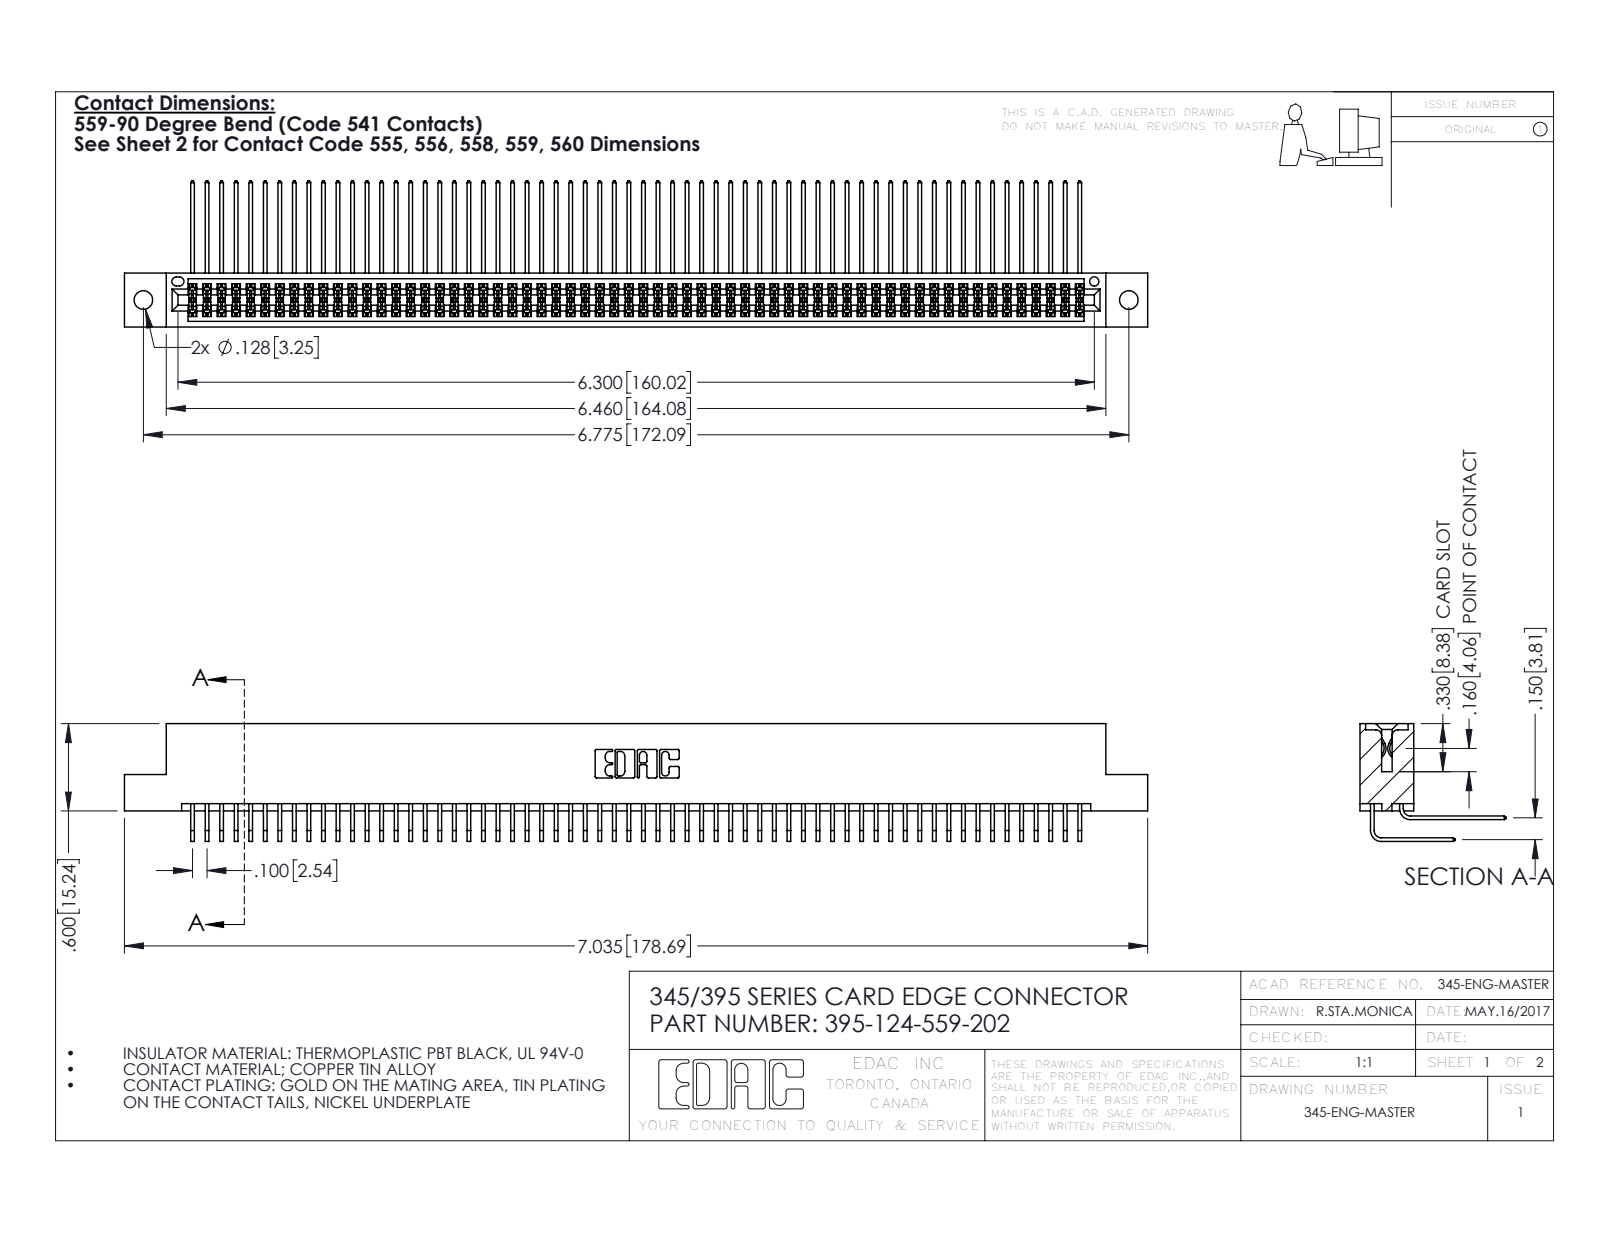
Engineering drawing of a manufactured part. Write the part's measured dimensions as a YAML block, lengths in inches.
part_name: "395-124-559-202; 345 Part_Flush Mounting Lugs - 0.128 Dia; 345-292-001_558 559 Tail - 1; 345-292-001_559 Tail - 2"
step_written_by: "SolidWorks 2016 (CONFIG_CONTROL_DESIGN)"
units: inches
bodies: {solids: 125, faces: 6574, planar: 4420, cylindrical: 2154, other: 0}
overall_size: [7.035, 1.005, 0.809]
volume: 1.112
surface_area: 47.14
round_holes:
  - {diameter: 0.128, count: 2}
  - {diameter: 0.064, count: 1}
partial_cylinders:
  - {radius: 0.006, count: 187}
  - {radius: 0.01, count: 22}
  - {radius: 0.007, count: 6}
  - {radius: 0.031, count: 6}
  - {radius: 0.026, count: 3}
  - {radius: 0.014, count: 2}
  - {radius: 0.019, count: 2}
  - {radius: 0.022, count: 2}
face_to_face_distances: [0.072, 0.298, 0.2, 0.37, 0.098, 0.272, 0.025, 0.225, 0.175, 0.15]
hole_center_spacings: [0.27, 6.539, 6.775]
